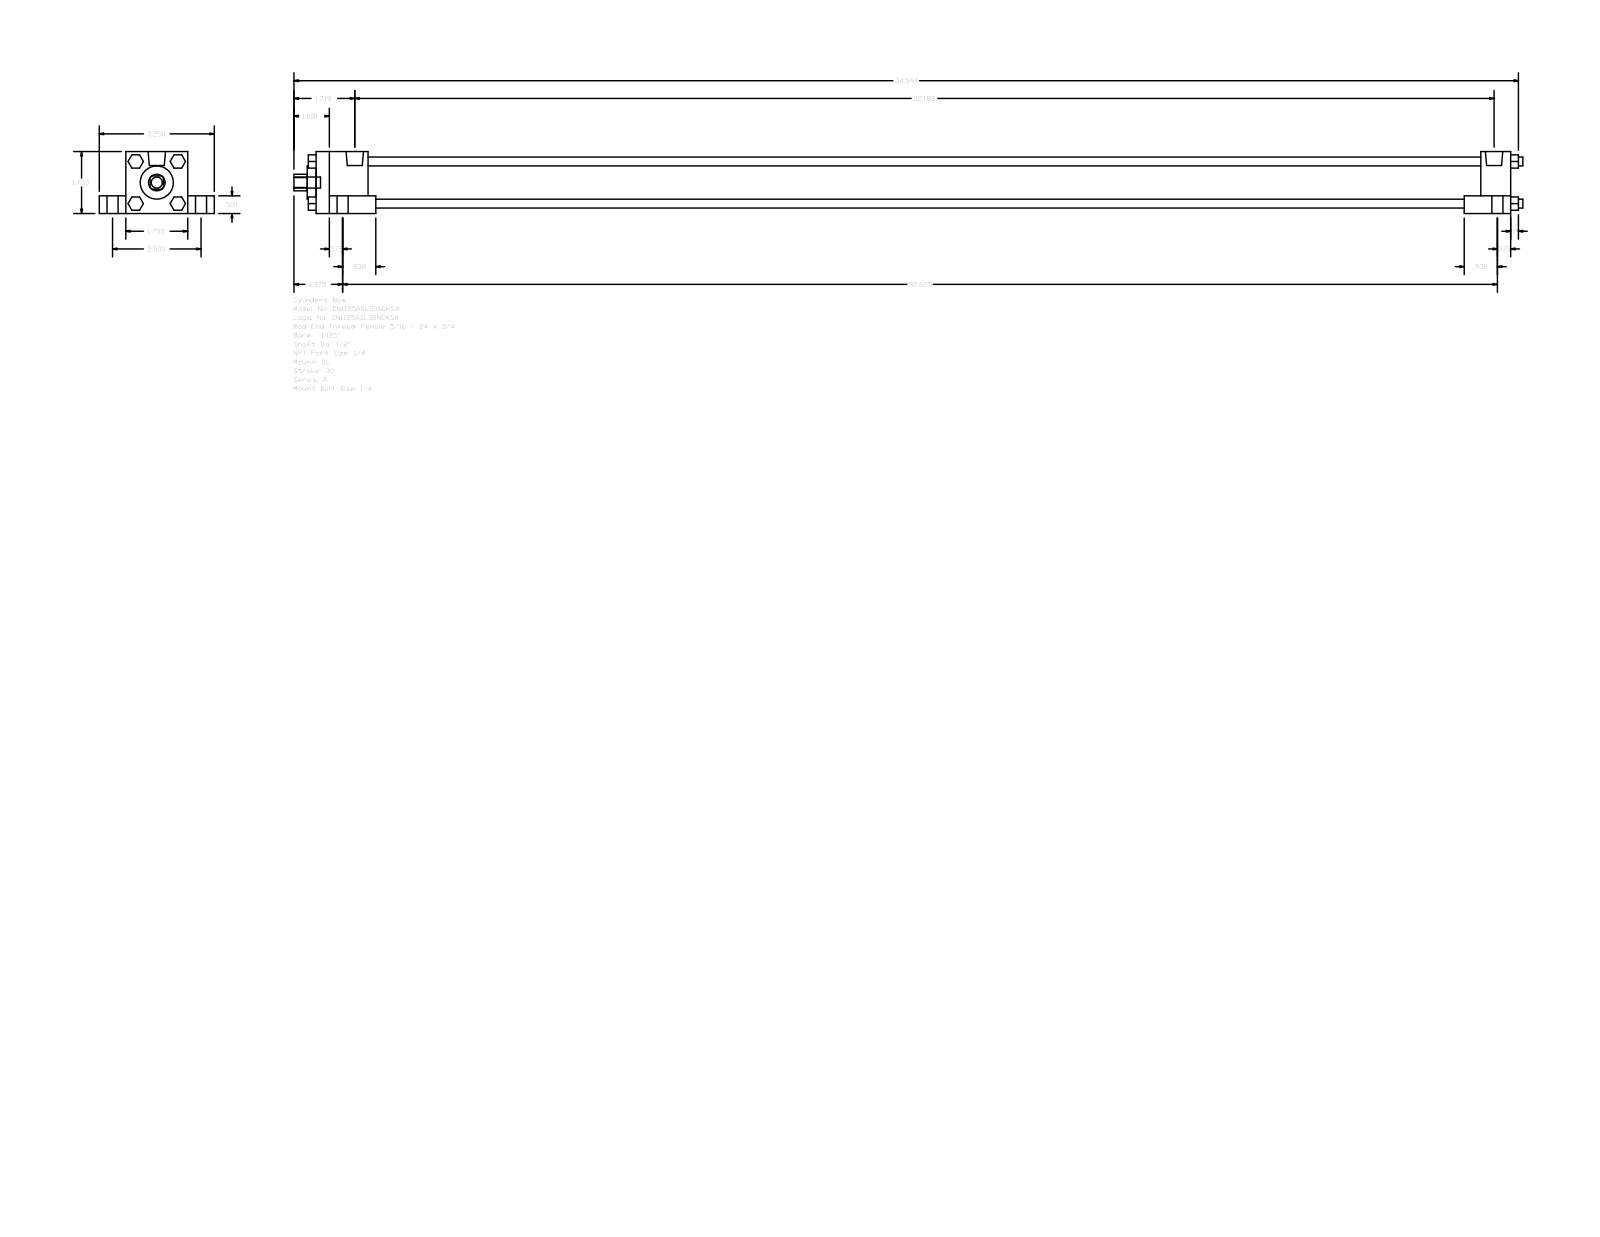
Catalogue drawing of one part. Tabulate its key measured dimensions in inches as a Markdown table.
| quantity | value |
| --- | --- |
| part name | A_SL__0112_0.5 |
| STEP written by | GSSL Pune (CONFIG_CONTROL_DESIGN) |
| units | inches |
| bodies | 0 solids, 150 faces (114 planar, 36 cylindrical, 0 other) |
| overall size | 34.719 × 3.25 × 1.75 |
| round holes (diameter × count) | 0.5 × 1, 0.937 × 1, 1.255 × 1 |
| round bosses / shafts (diameter × count) | 0.313 × 5, 0.563 × 4, 0.25 × 4, 0.219 × 4, 0.492 × 2 |
| partial cylindrical surfaces (radius × count) | 0.234 × 1 |
| main face-to-face distances | 1.75, 1.25, 0.5, 0.75, 2.5, 32.281, 33.75, 32.906, 0.844, 1.469 |
